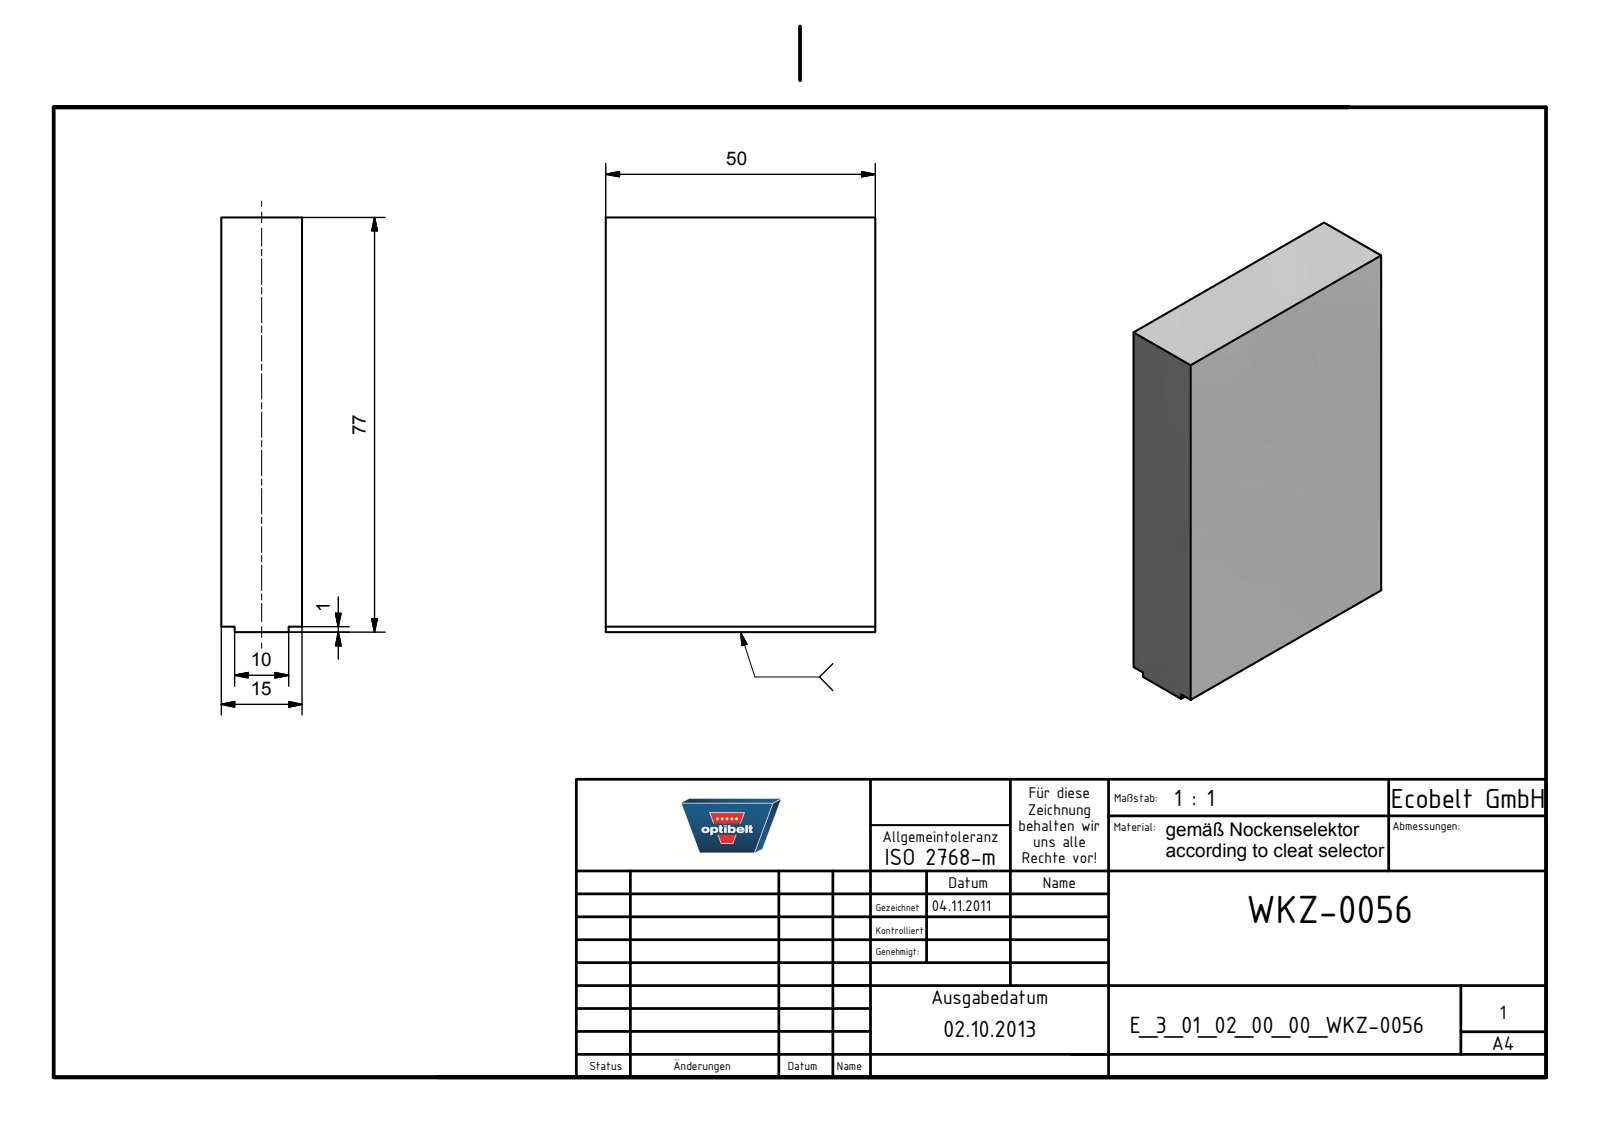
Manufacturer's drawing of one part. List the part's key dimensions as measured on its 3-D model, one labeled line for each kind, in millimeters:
Part name (STEP PRODUCT): E_3_01_02_00_00_WKZ-0056
STEP written by: Autodesk Inventor 2021 (AUTOMOTIVE_DESIGN)
Units: millimetres
Bodies: 1 solid, 10 faces (10 planar, 0 cylindrical, 0 other)
Overall size (bounding box): 77 × 50 × 15
Volume: 57 500 mm³ · Surface area: 11 500 mm²
Main face-to-face distances: 15, 50, 77, 1, 76, 2.5, 12.5, 10
